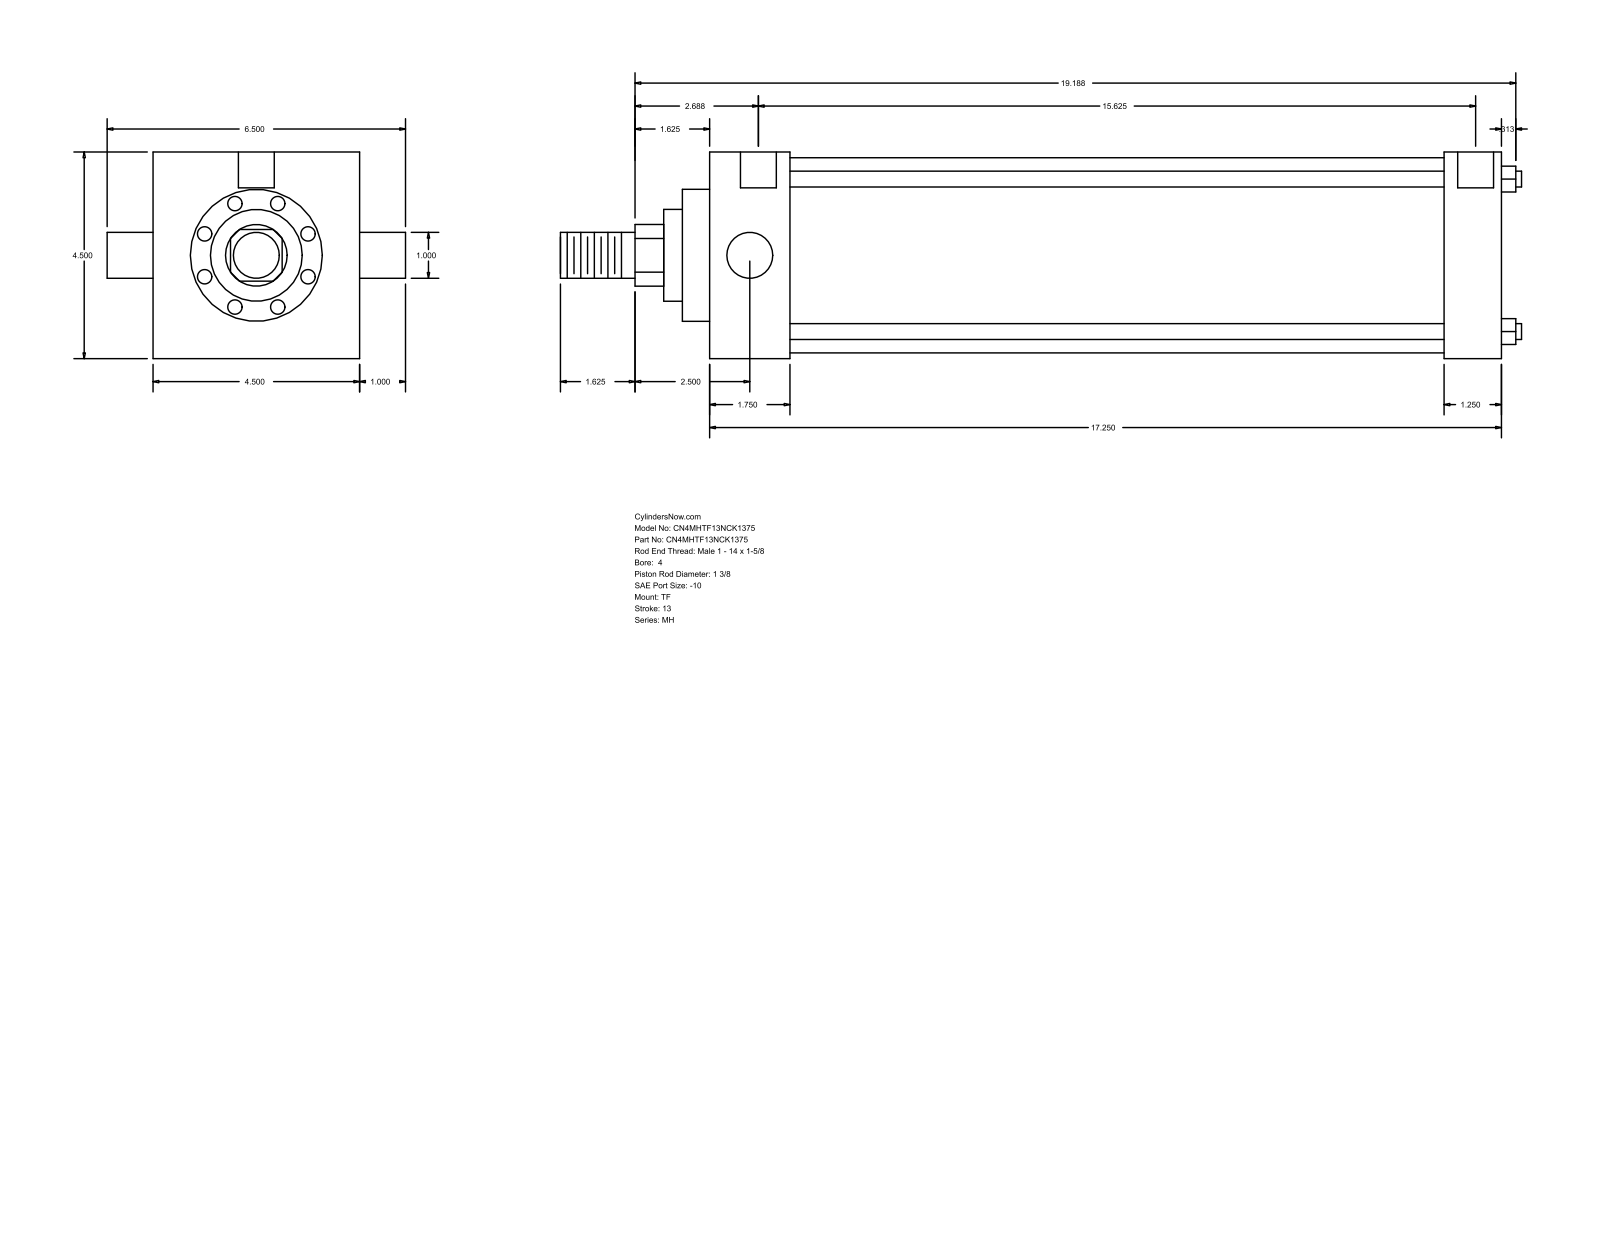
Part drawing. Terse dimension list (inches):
name: MH_TF__0400_1.375
written by: GSSL Pune (CONFIG_CONTROL_DESIGN)
unit: in
bodies: 0 solids, 86 faces (61 planar, 25 cylindrical, 0 other)
size: 20.937 × 6.5 × 4.5
holes: 3× ⌀0.344, 2× ⌀0.781
bosses: 4× ⌀0.345, 2× ⌀1, 1× ⌀4.25, 1× ⌀2.875, 1× ⌀2, 1× ⌀1.375
rounds: 1× R0.672
face distances: 4.5, 17.25, 1.75, 15.5, 16, 14.25, 1.25, 0.594, 2.344, 16.594
hole spacings: 0.063, 15.688, 15.625, 15.75
